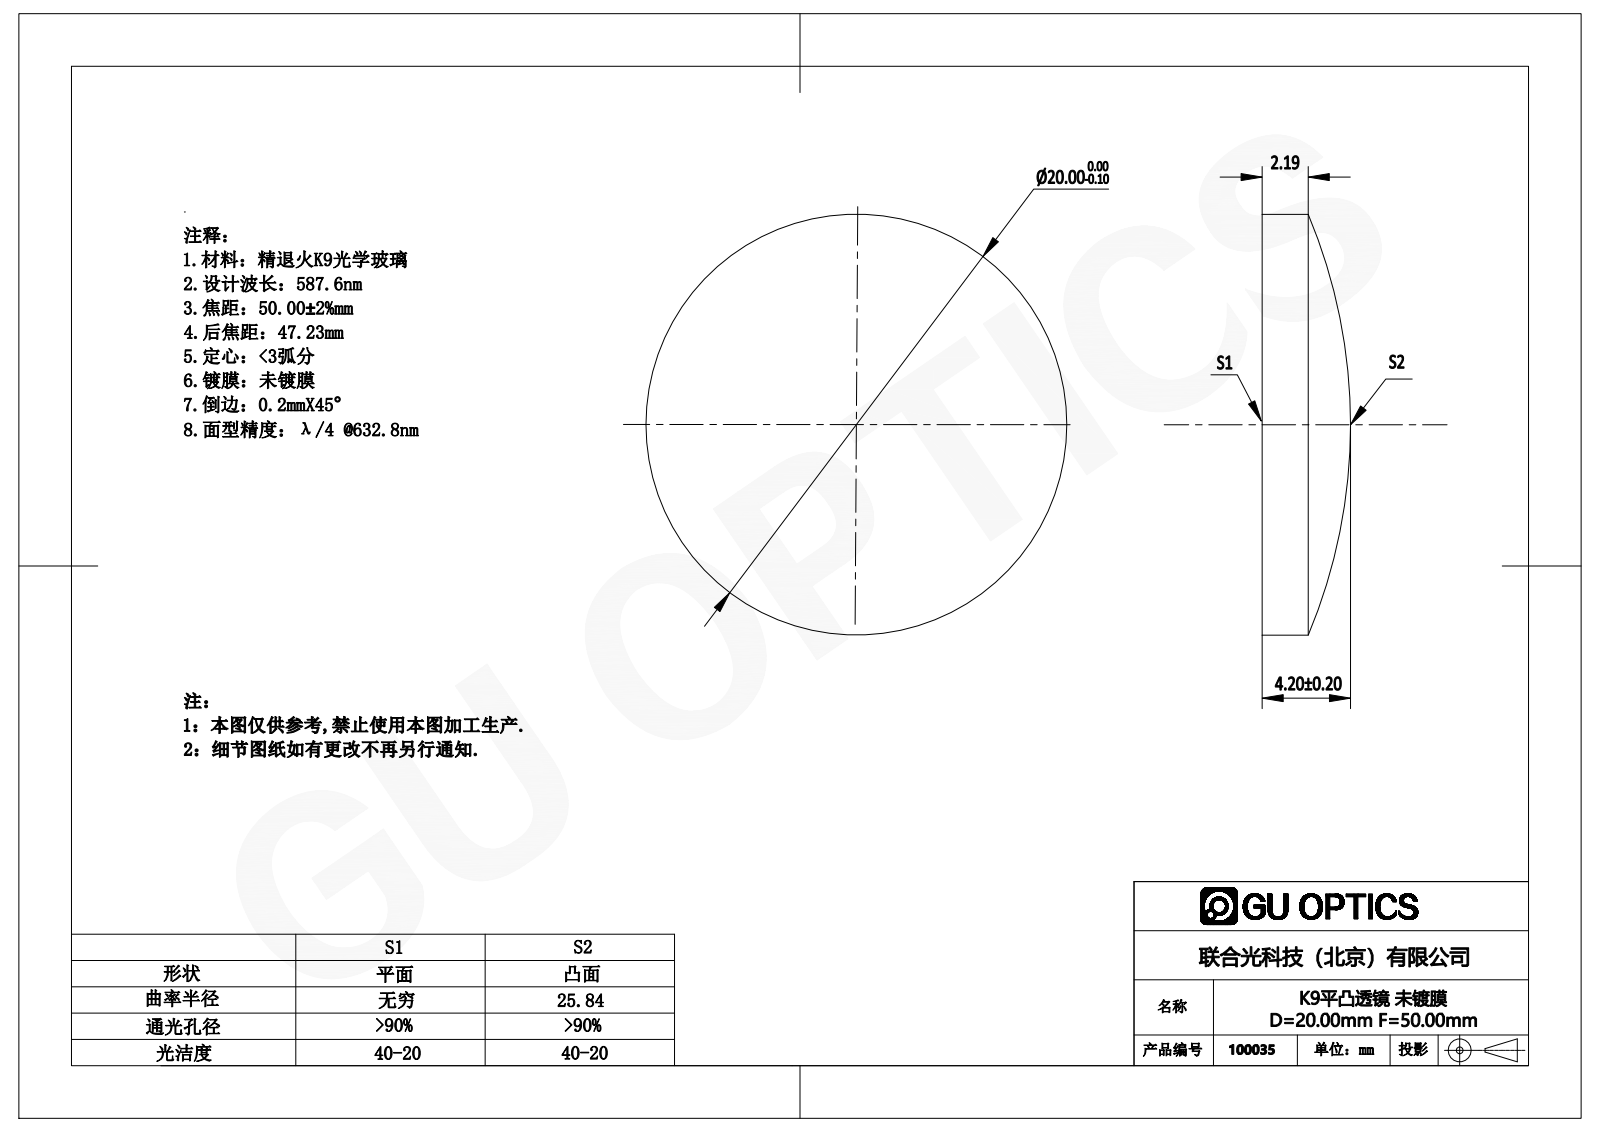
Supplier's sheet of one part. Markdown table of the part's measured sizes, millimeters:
| quantity | value |
| --- | --- |
| part name | 100035 |
| STEP written by | SolidWorks 2016 (AUTOMOTIVE_DESIGN) |
| units | millimeters |
| bodies | 1 solid, 5 faces (1 planar, 2 cylindrical, 2 other) |
| overall size | 20 × 20 × 4.2 |
| volume | 1 008 mm³ |
| surface area | 779 mm² |
| round bosses / shafts (diameter × count) | 20 × 1 |
